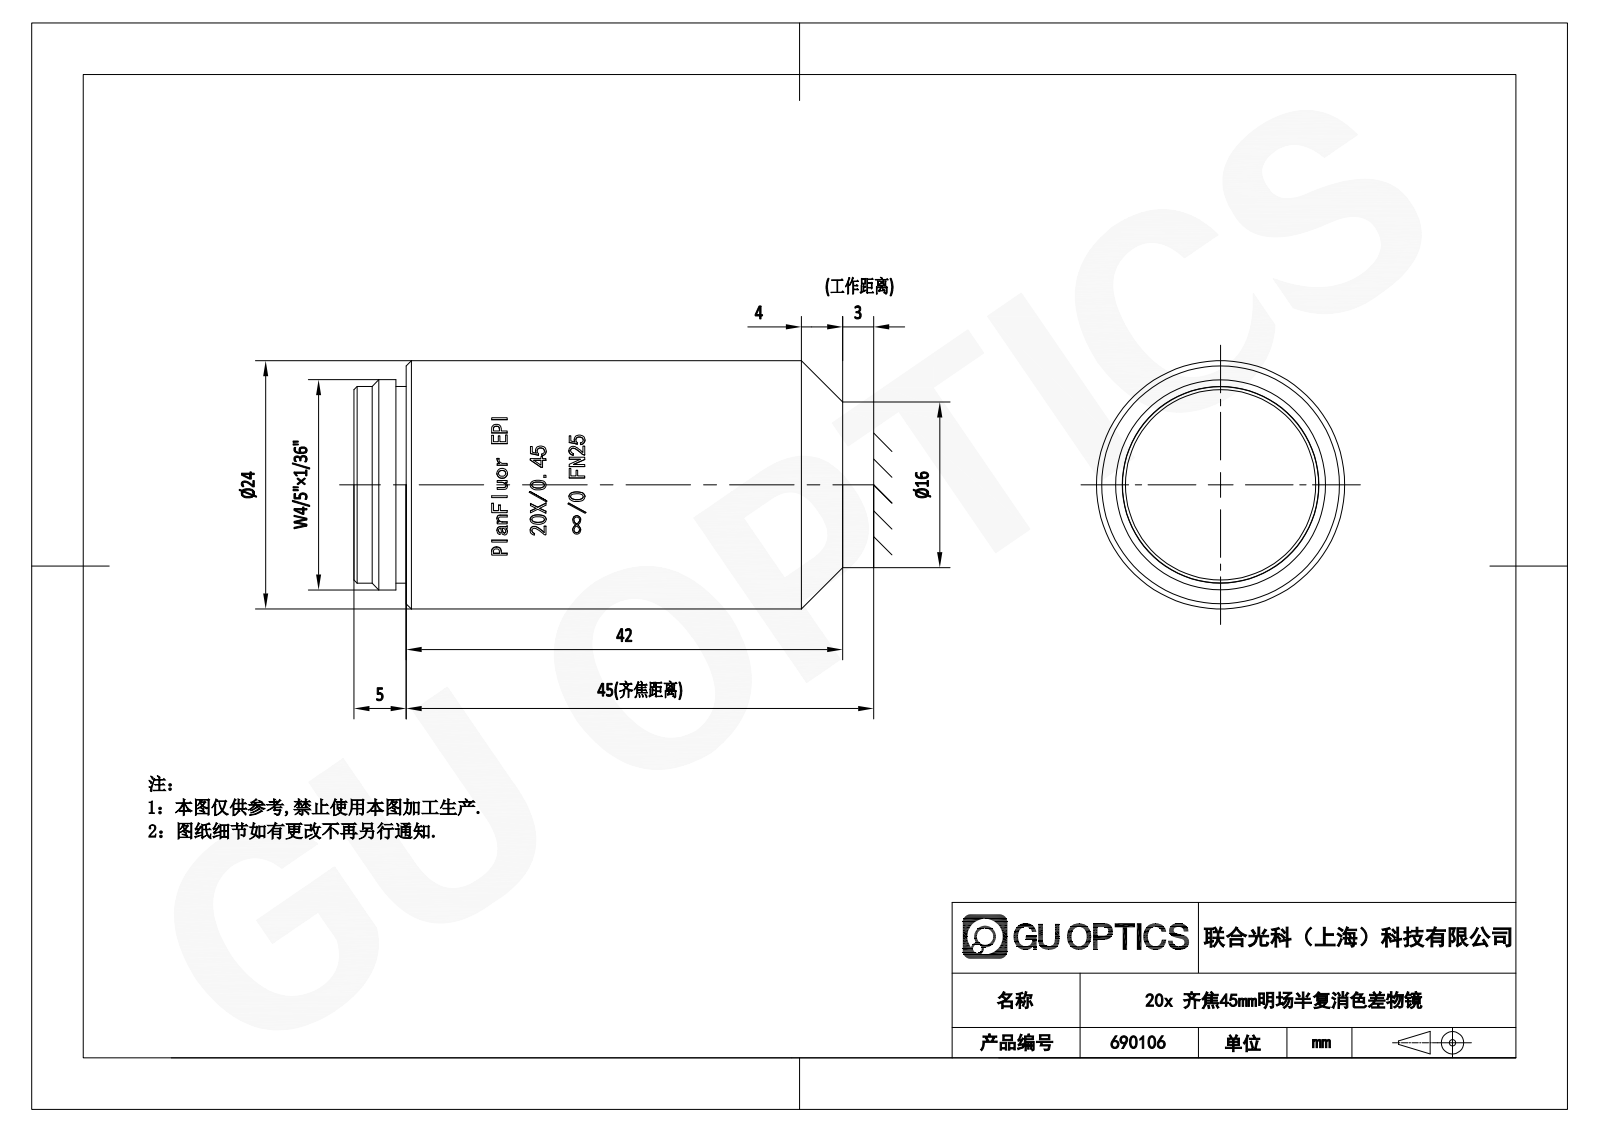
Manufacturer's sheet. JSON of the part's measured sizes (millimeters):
{"part_name": "690106", "step_written_by": "SolidWorks 2020 (CONFIG_CONTROL_DESIGN)", "units": "millimeters", "bodies": {"solids": 1, "faces": 307, "planar": 139, "cylindrical": 45, "other": 123}, "overall_size": [47.25, 24.05, 24], "volume_mm3": 20055, "surface_area_mm2": 4231, "round_bosses_or_shafts": [[24, 1], [20.32, 1], [19, 1]], "partial_cylinders_radius": [[12.05, 1]], "face_to_face_distances": [47.25, 5.05, 42.2, 1, 4.05, 43.2, 1.75, 2.3, 3.3, 45.5]}
